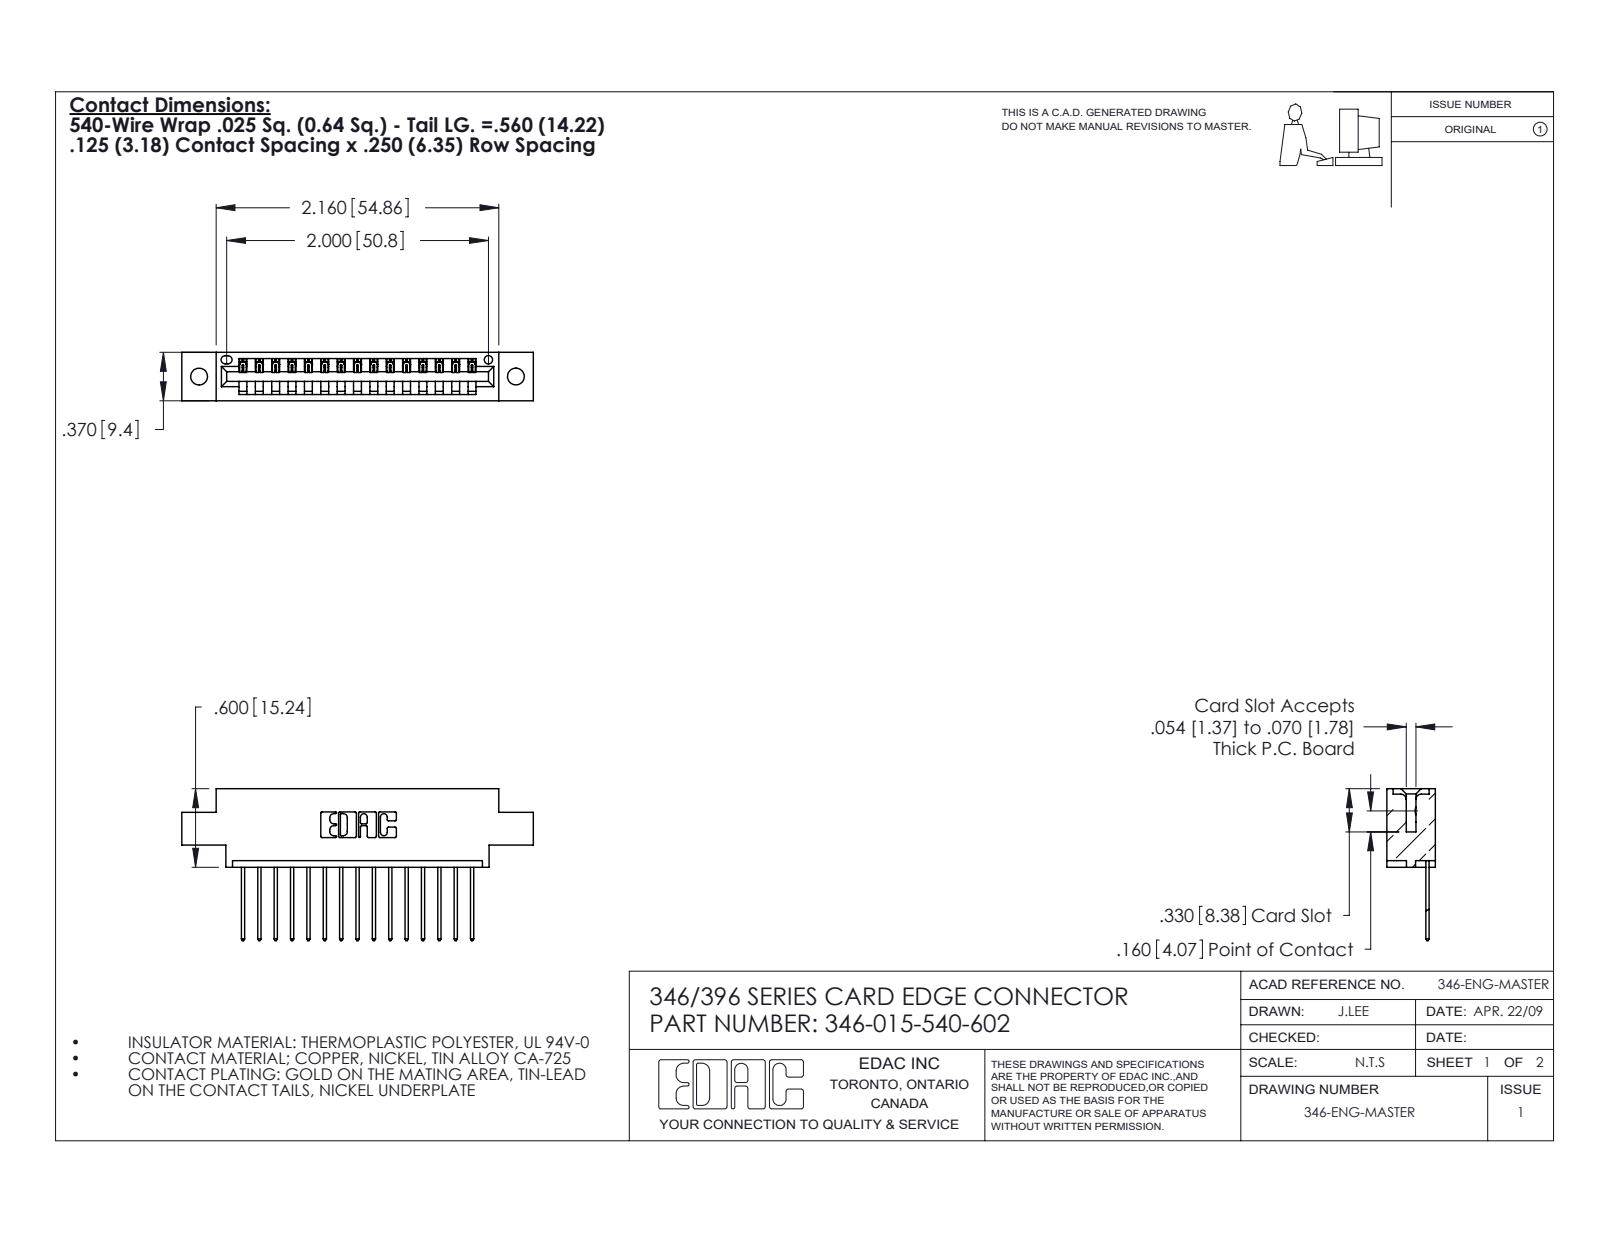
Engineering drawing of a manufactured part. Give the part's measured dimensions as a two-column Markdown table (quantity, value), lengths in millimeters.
| quantity | value |
| --- | --- |
| part name | 346 Part_0.170 Offset - 0.128 Dia; 345-292-001_345-293-140; 346-015-540-602 |
| STEP written by | SolidWorks 2020 (CONFIG_CONTROL_DESIGN) |
| units | millimeters |
| bodies | 16 solids, 996 faces (680 planar, 316 cylindrical, 0 other) |
| overall size | 68.2 × 29.5 × 9.4 |
| volume | 6 180 mm³ |
| surface area | 7 458 mm² |
| round holes (diameter × count) | 3.3 × 2, 1.6 × 1 |
| partial cylindrical surfaces (radius × count) | 0.2 × 30, 0.3 × 30, 0.3 × 22, 0.2 × 6, 0.8 × 6, 0.7 × 3, 0.8 × 2, 1 × 2 |
| main face-to-face distances | 1.2, 8.2, 9.4, 6.4, 1.8, 7.6, 0.6, 3.8, 5.6, 2.5 |
| hole center spacings | 6.2, 56.2, 61.5 |
